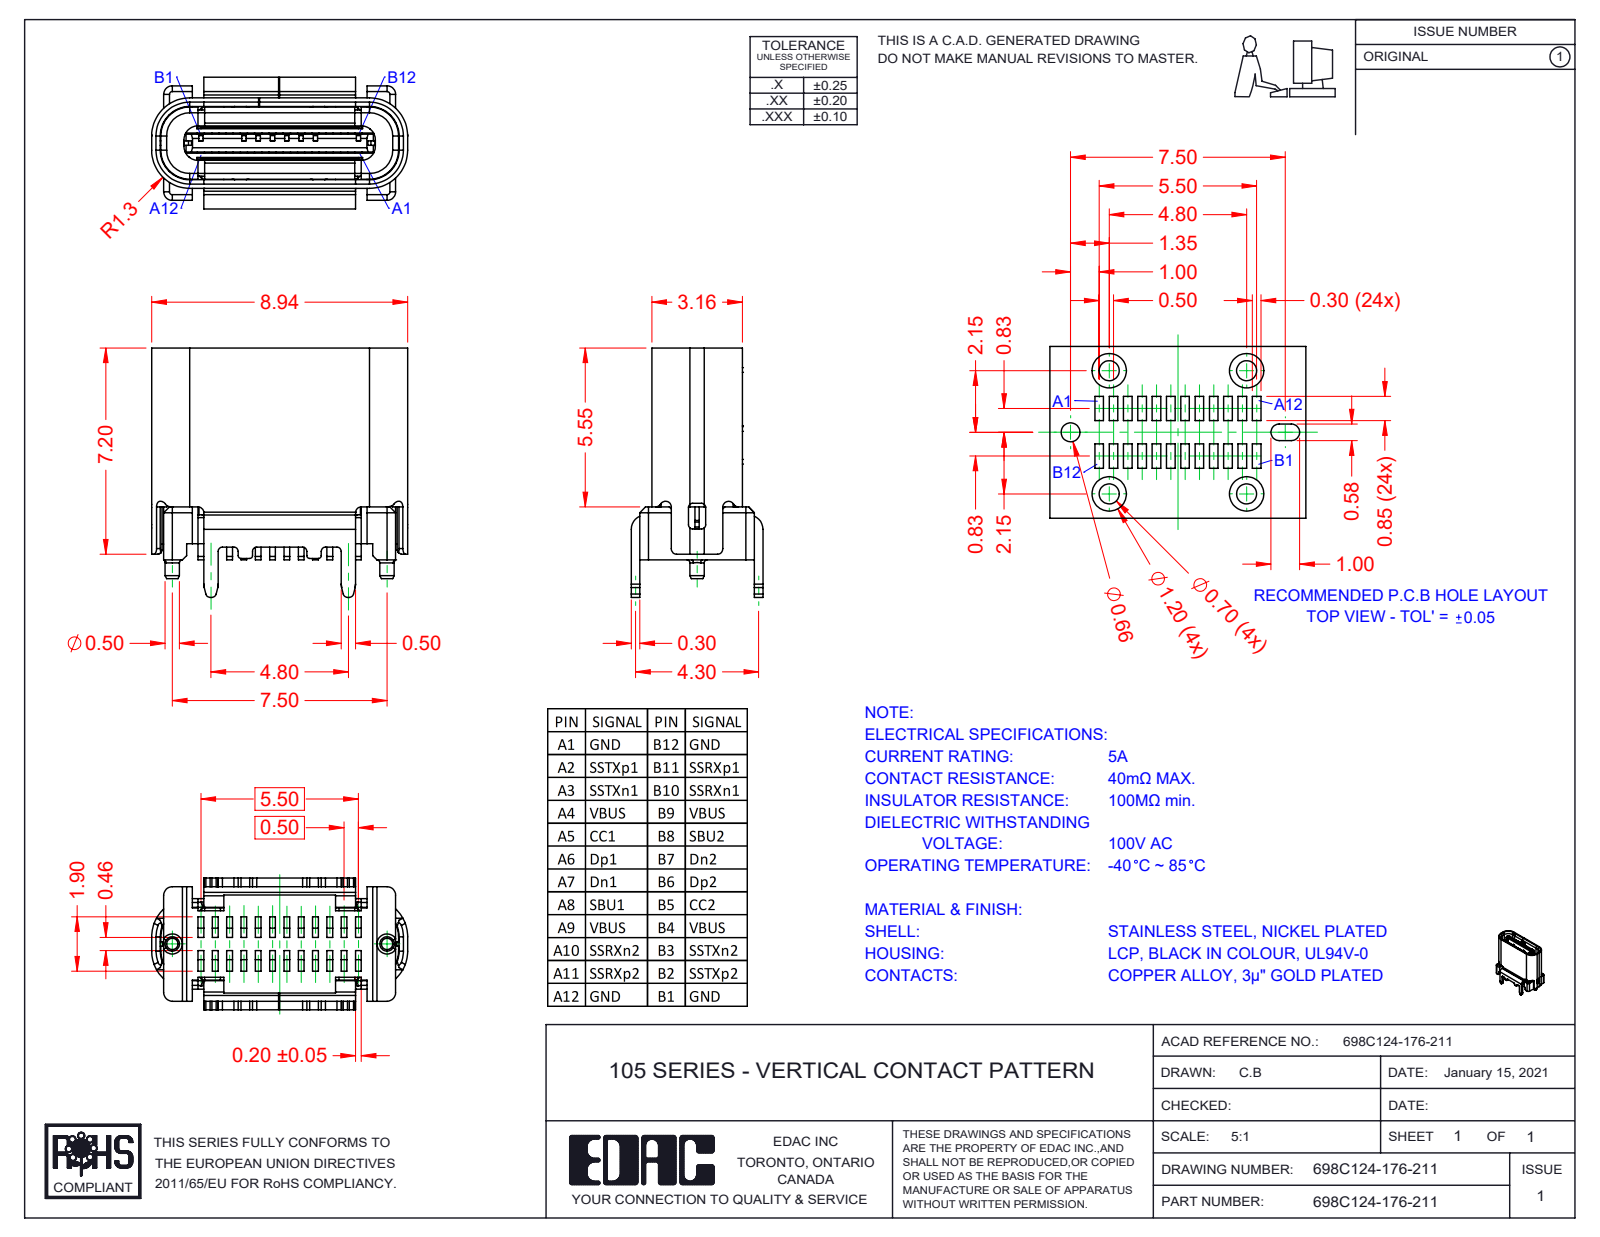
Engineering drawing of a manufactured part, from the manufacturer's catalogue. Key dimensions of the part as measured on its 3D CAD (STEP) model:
Part name (STEP PRODUCT): Shell 698C124-176-211; Shell2 698C124-176-211; Insulator 698C124-176-211; 698C124-176-211
STEP written by: SolidWorks 2020 (AUTOMOTIVE_DESIGN)
Units: millimetres
Bodies: 4 solids, 1222 faces (862 planar, 324 cylindrical, 36 other)
Overall size (bounding box): 8.94 × 8.71 × 4.6
Volume: 123 mm³ · Surface area: 611 mm²
Round holes (diameter × count): ⌀0.35 ×2
Round bosses / shafts (diameter × count): ⌀0.5 ×2
Partial cylindrical surfaces — rounded edges, fillets, slot ends (radius × count): R0.1 ×50, R0.2 ×29, R0.15 ×22, R0.5 ×10, R0.3 ×8, R0.13 ×6, R0.4 ×4, R1 ×4
Main face-to-face distances: 2.86, 0.66, 0.42, 3.16, 0.81, 2.56, 0.85, 1.78, 1.08, 2.08
Hole centre spacings: 3.48
